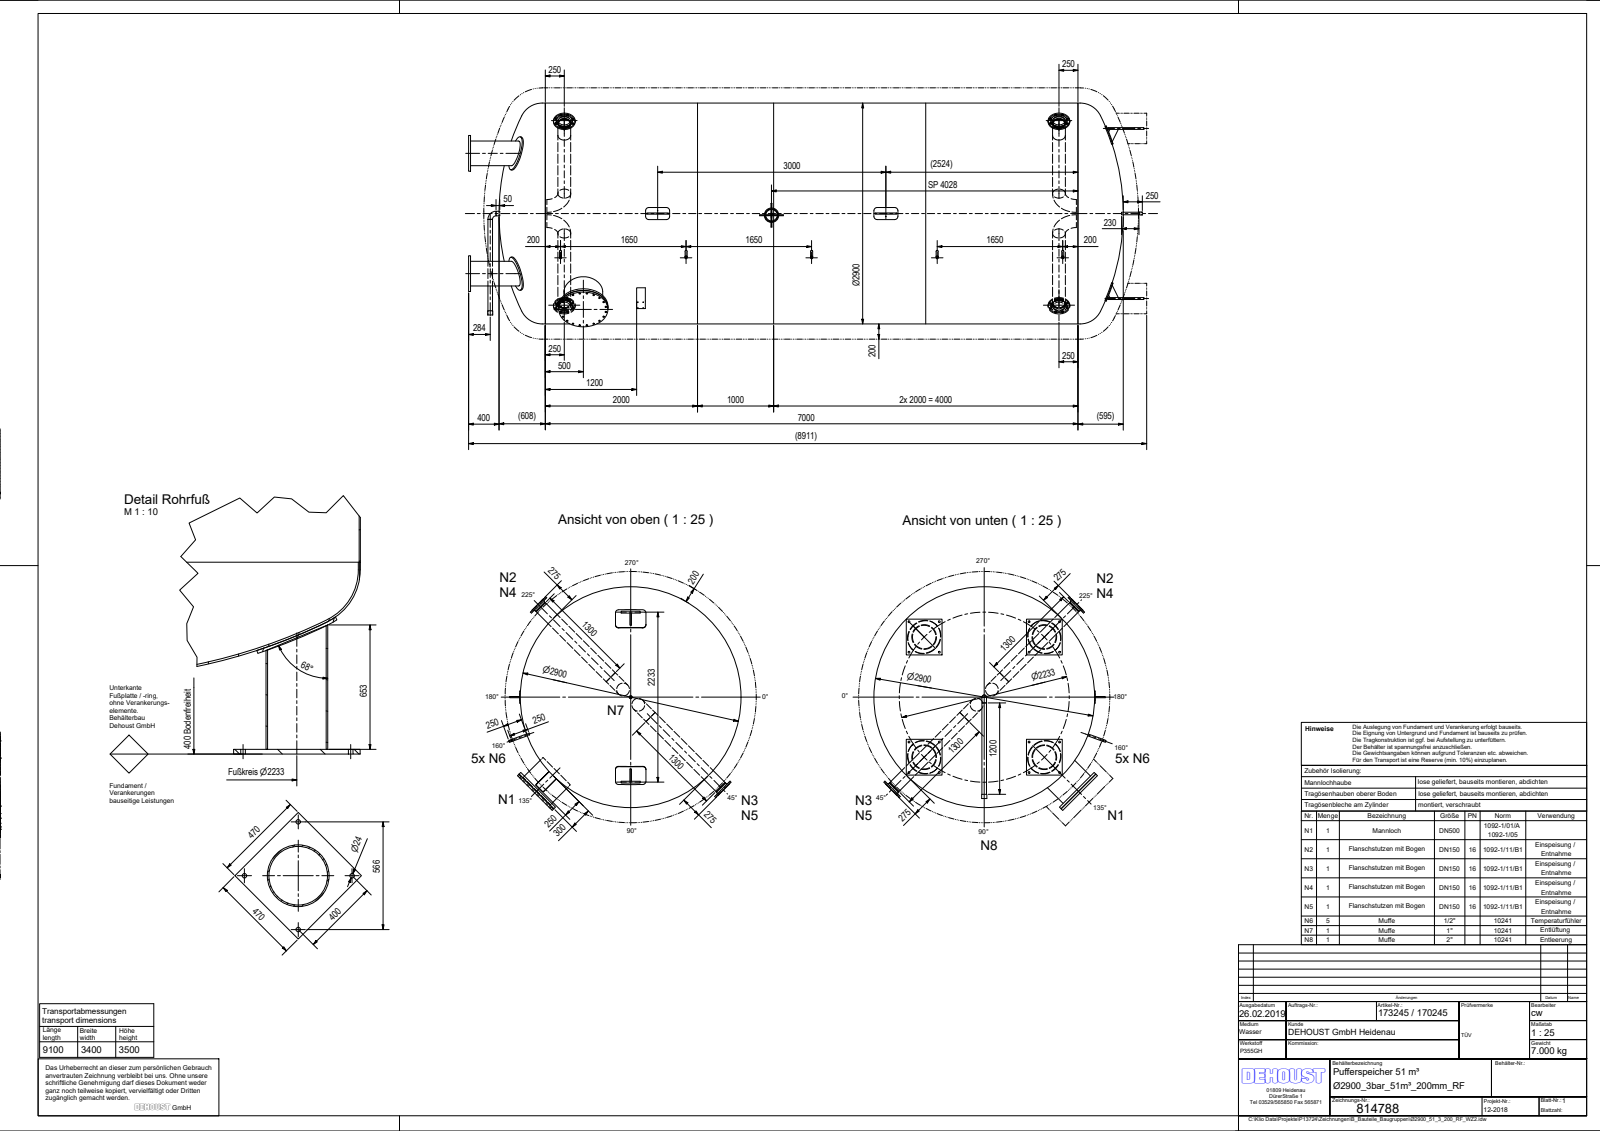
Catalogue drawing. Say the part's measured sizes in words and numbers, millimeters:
The part is named "Ø2900_51_3_200_RF_WZ2; Klöpper_Gew_Ø2900_7,5; Klöpper_Gew_Ø2900_10,3; Zyl_Ø2900_6x7000_2019 (+8 more)". Its 3-D file was written by "Autodesk Inventor 2019 (AUTOMOTIVE_DESIGN)". It is 58 solids with 449 faces: 178 planar, 225 cylindrical and 46 other. Overall it measures 8874.42 by 3051.99 by 2937.4 millimeters. Its volume is 810 900 000 cubic millimeters and its surface area 183 400 000 square millimeters. Round holes: 64 of diameter 22, 16 of diameter 24, 8 of diameter 159.3, 5 of diameter 18.63, 5 of diameter 21.7, 5 of diameter 26.9, 4 of diameter 5.8, 4 of diameter 168.3, 4 of diameter 307.9, 2 of diameter 5, 2 of diameter 52.3, 2 of diameter 508. Round bosses or shafts: 8 of diameter 168.3, 5 of diameter 26.9, 5 of diameter 26.4, 4 of diameter 450, 4 of diameter 323.9, 4 of diameter 285, 4 of diameter 212, 1 of diameter 2900. Partial cylindrical surfaces (rounded edges, fillets, slot ends): 16 of radius 42, 6 of radius 10, 4 of radius 6, 2 of radius 5, 2 of radius 36, 2 of radius 72, 1 of radius 125, 1 of radius 1460. The main face-to-face distances are 25, 600, 500, 4257.96, 4757.96, 4232.96, 4732.96, 27.99, 3250, 3750. The hole center spacings are 120, 300, 185.41, 93.86, 1650, 6500, 352.67, 169.71.
